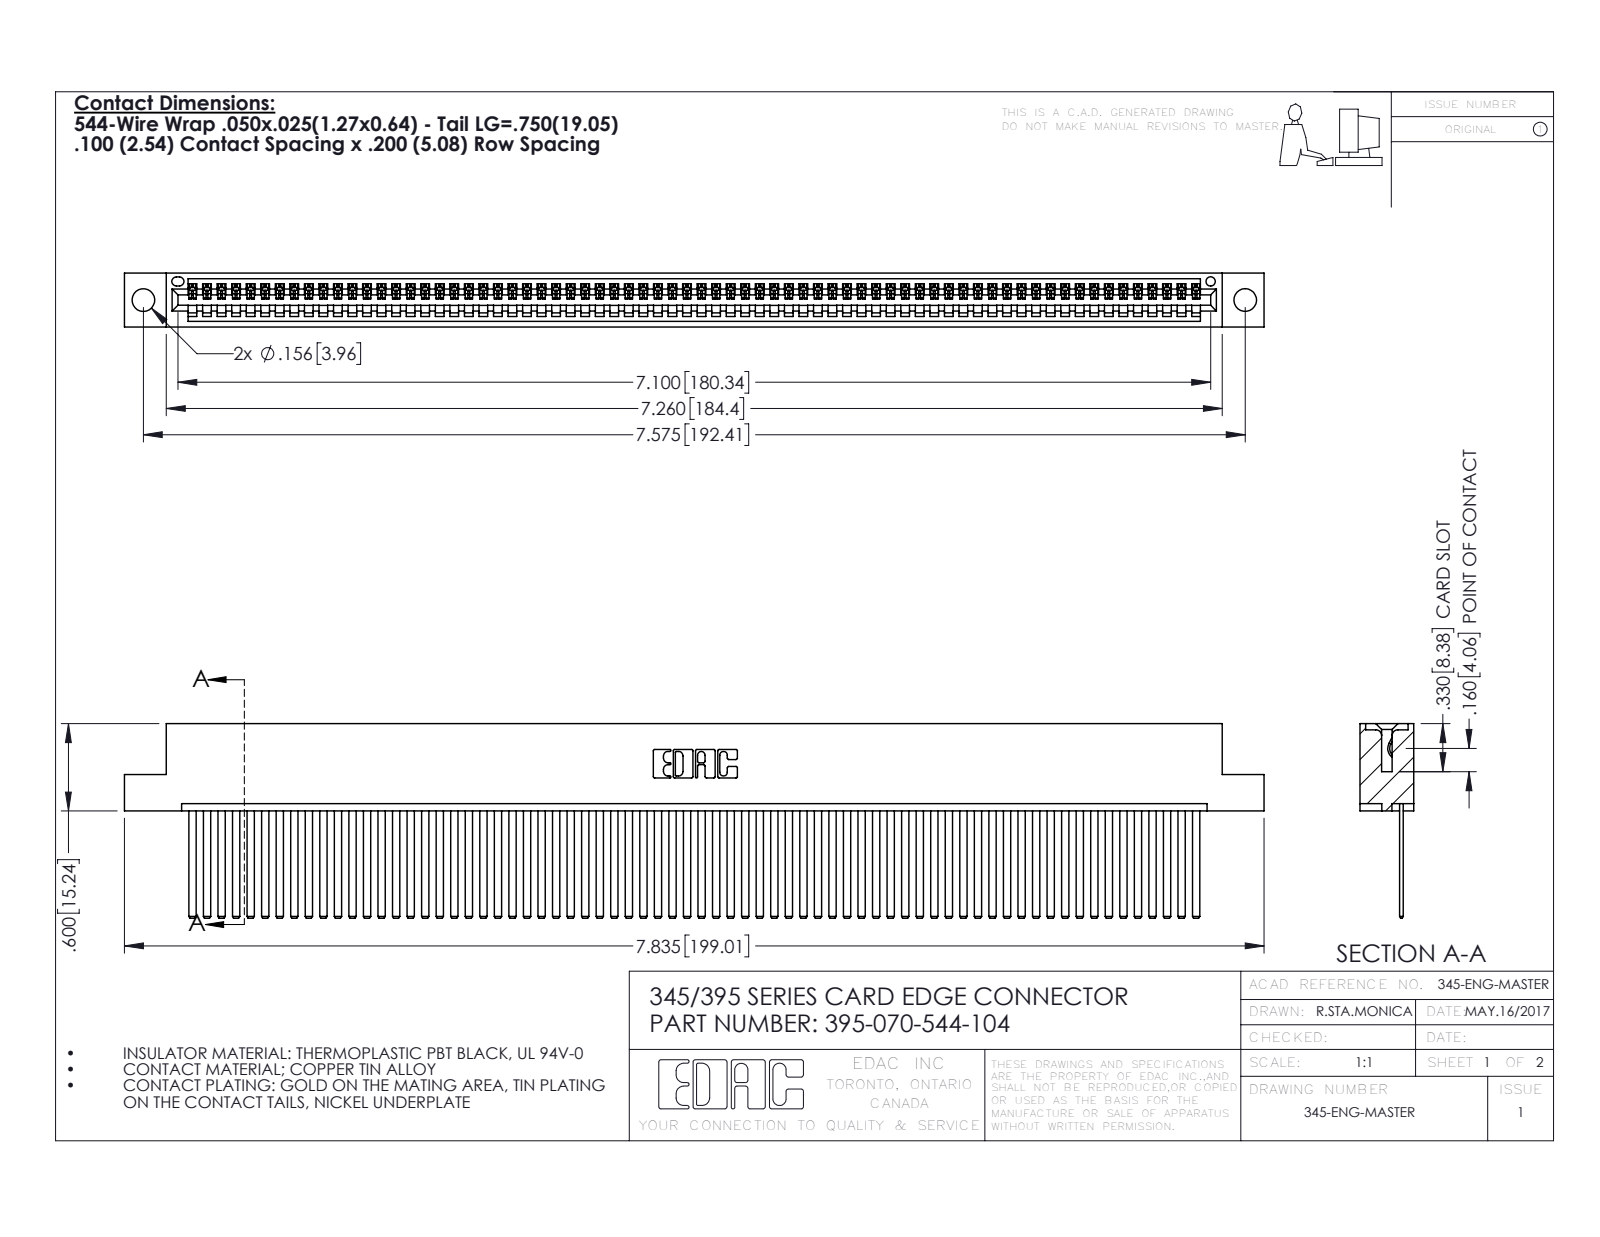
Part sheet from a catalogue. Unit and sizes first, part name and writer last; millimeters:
Units: millimetres
Overall size (bounding box): 199 × 34 × 9.4
Round holes (diameter × count): ⌀4 ×2, ⌀1.6 ×1
Partial cylindrical surfaces — rounded edges, fillets, slot ends (radius × count): R0.2 ×140, R0.3 ×22, R0.2 ×6, R0.8 ×6, R0.7 ×3, R0.8 ×2, R1 ×2, R0.4 ×1
Main face-to-face distances: 1.8, 7.6, 0.6, 2.5, 6.9, 9.4, 5.1, 5.7, 3.8, 1.8
Hole centre spacings: 6.9, 186.4, 192.4
Volume: 19 860 mm³ · Surface area: 29 010 mm²
Bodies: 71 solids, 3766 faces (2600 planar, 1166 cylindrical, 0 other)
Part name (STEP PRODUCT): 345 Part_Flush Mounting Lugs - 0.156 Dia-TH; 395-070-544-104; 345-292-001_345-293-144
STEP written by: SolidWorks 2016 (CONFIG_CONTROL_DESIGN)
